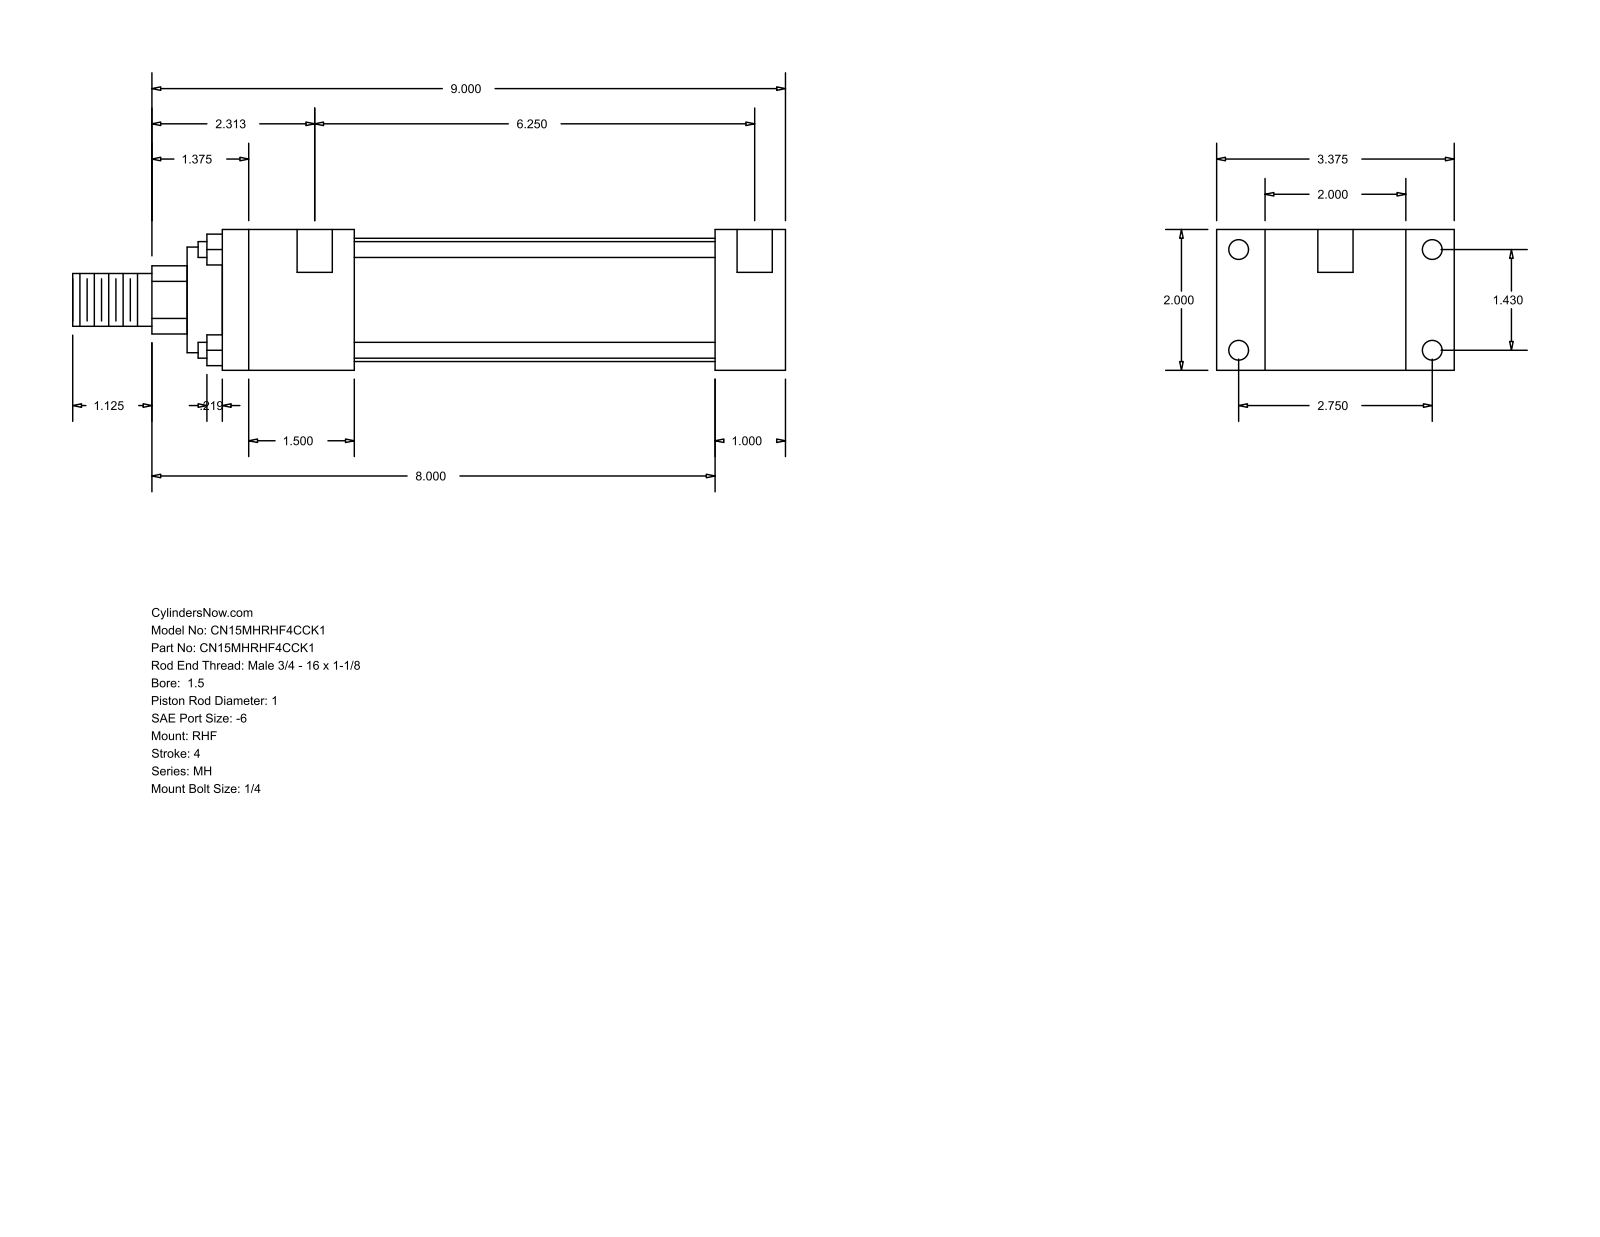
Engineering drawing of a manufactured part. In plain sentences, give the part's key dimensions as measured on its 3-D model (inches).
The part is named "MH_RHF__0150_1". Its 3-D file was written by "GSSL Pune (CONFIG_CONTROL_DESIGN)". It is 0 solids with 88 faces: 60 planar, 28 cylindrical and 0 other. Overall it measures 10.125 by 3.375 by 2 inches. Round holes: 4 of diameter 0.219, 4 of diameter 0.281, 2 of diameter 0.5. Round bosses or shafts: 4 of diameter 0.225, 1 of diameter 1.75, 1 of diameter 1.5, 1 of diameter 1, 1 of diameter 0.75. Partial cylindrical surfaces (rounded edges, fillets, slot ends): 1 of radius 0.484. The main face-to-face distances are 2, 1, 0.687, 2.687, 3.375, 8, 7, 1.875, 5.125, 6.125. The hole center spacings are 1.43, 2.75, 3.099, 6.375, 0.125, 6.25.
